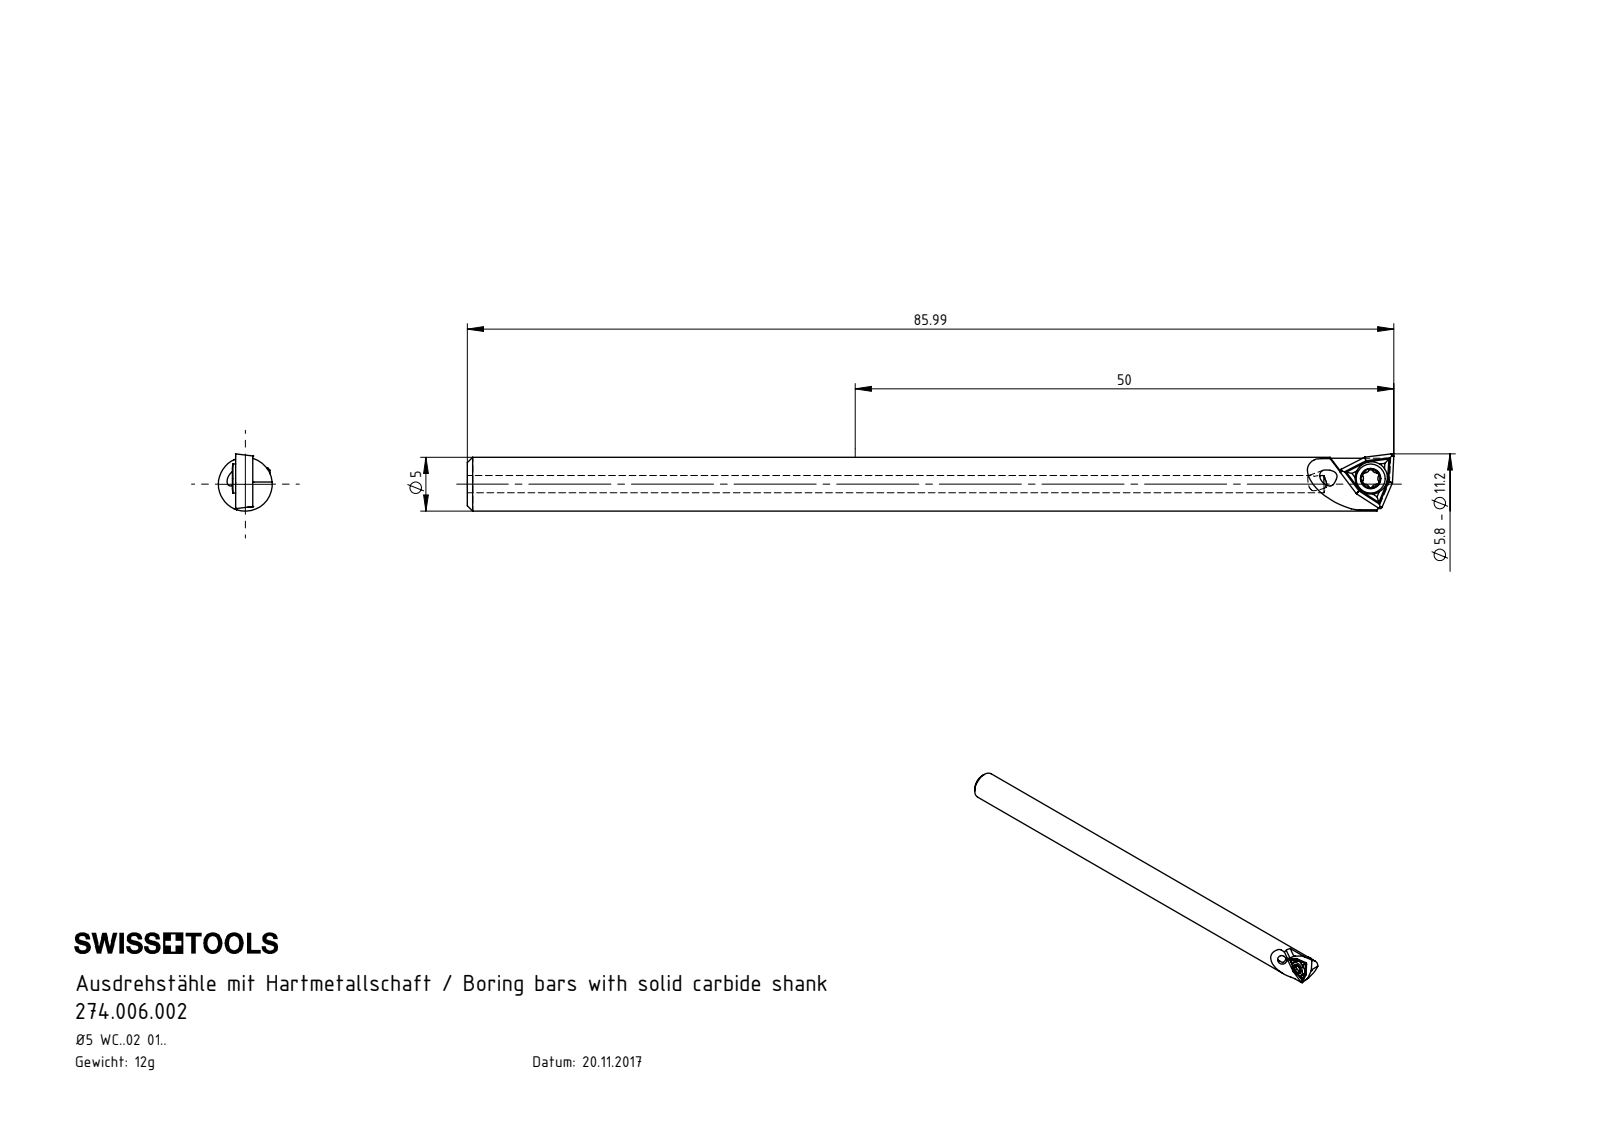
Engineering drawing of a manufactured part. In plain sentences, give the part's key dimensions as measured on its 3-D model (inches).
The part is named "SFS-Torx-M2; 274.006.002; WCMT020102; B06-WWA.K11.080_A". Its 3-D file was written by "SolidWorks 2017 (CONFIG_CONTROL_DESIGN)". It is 3 solids with 106 faces: 36 planar, 33 cylindrical and 37 other. Overall it measures 3.385 by 0.209 by 0.197 inches. Its volume is 0.09 cubic inches and its surface area 2.874 square inches. Round holes: 3 of diameter 0.063, 1 of diameter 0.091, 1 of diameter 0.118. Round bosses or shafts: 1 of diameter 0.197, 1 of diameter 0.106, 1 of diameter 0.079. Partial cylindrical surfaces (rounded edges, fillets, slot ends): 6 of radius 0.008, 6 of radius 0.014, 1 of radius 0.031. The main face-to-face distances are 0.059, 0.055, 0.063, 0.118, 0.122, 0.126, 0.063, 0.138, 0.074, 0.02.
